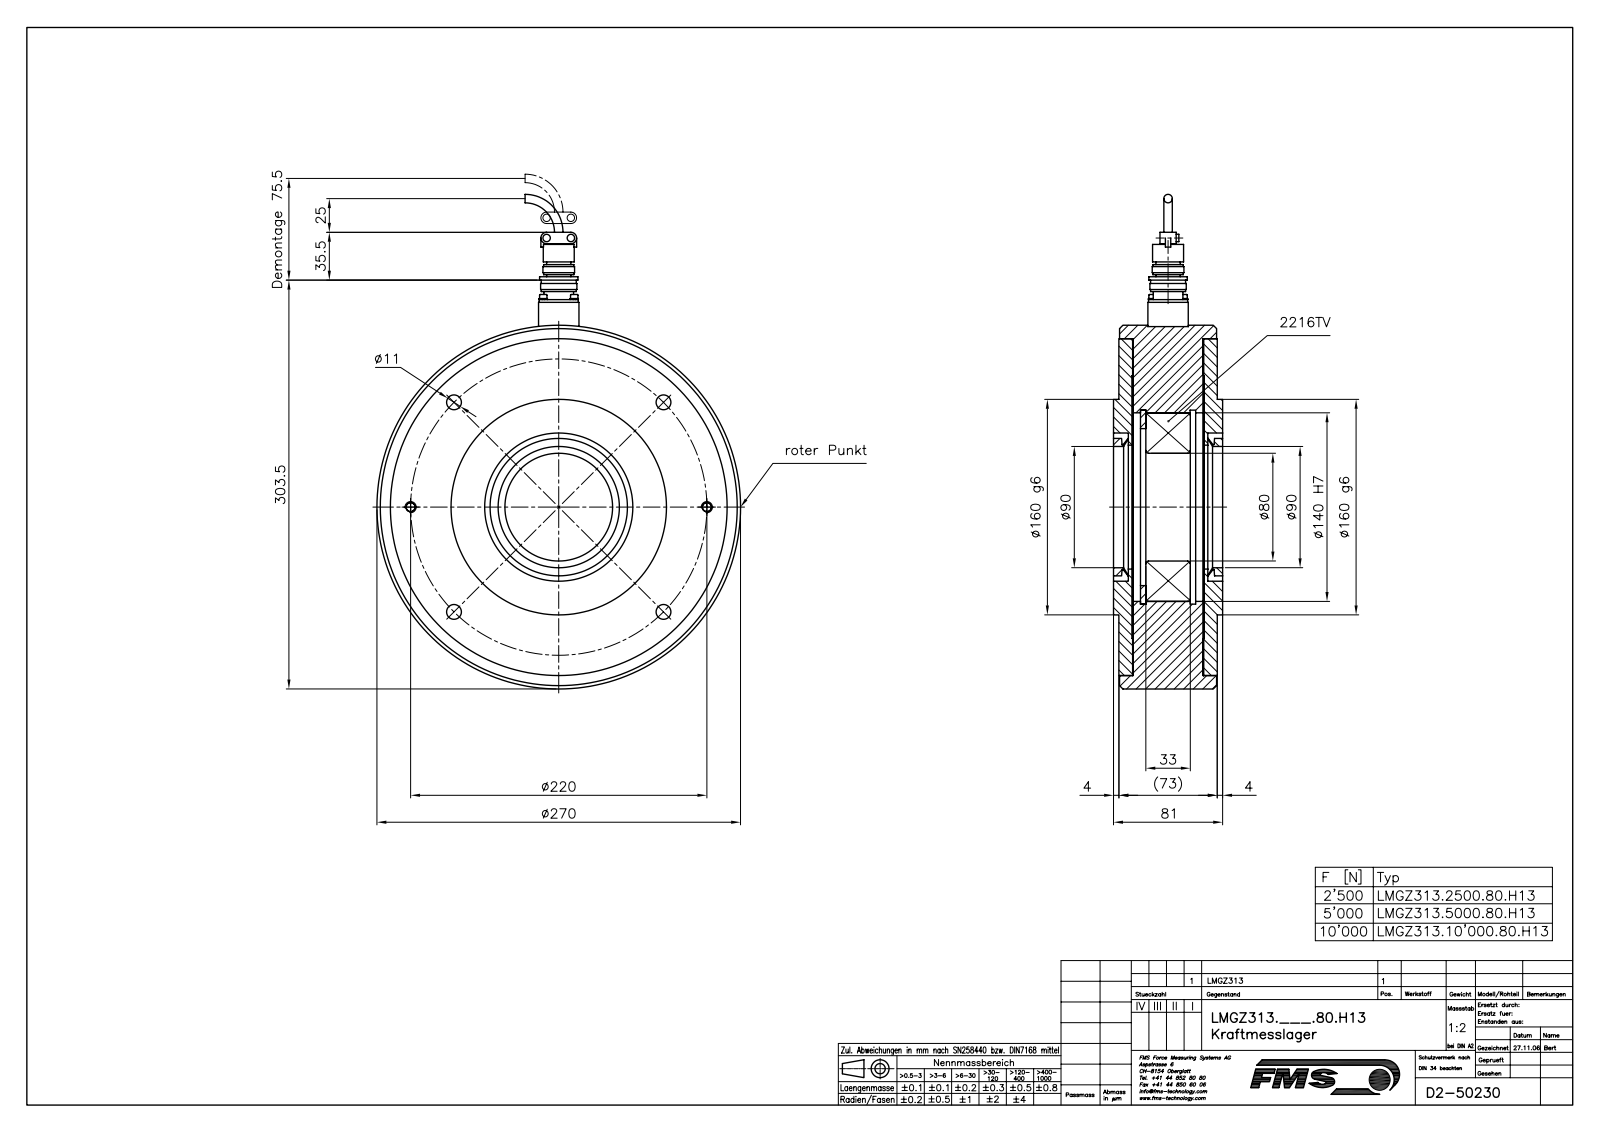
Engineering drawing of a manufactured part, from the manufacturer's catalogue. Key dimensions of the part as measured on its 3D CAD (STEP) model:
Part name (STEP PRODUCT): L50230; L4926704; TEIL1; L49342 (+8 more)
STEP written by: Mechanical Desktop 2007 (CONFIG_CONTROL_DESIGN)
Units: millimetres
Bodies: 21 solids, 398 faces (104 planar, 232 cylindrical, 62 other)
Overall size (bounding box): 367.15 × 320.5 × 270
Volume: 3 620 000 mm³ · Surface area: 569 668 mm²
Round holes (diameter × count): ⌀2.6 ×4, ⌀3.2 ×4, ⌀3.4 ×4, ⌀11 ×4, ⌀12 ×4, ⌀6.91 ×2, ⌀9 ×2, ⌀10 ×2, ⌀15 ×2, ⌀23 ×1, ⌀80 ×1, ⌀90 ×1
Round bosses / shafts (diameter × count): ⌀5.5 ×6, ⌀6.2 ×4, ⌀3 ×4, ⌀2.5 ×4, ⌀13 ×2, ⌀8 ×2, ⌀270 ×1, ⌀250 ×1
Partial cylindrical surfaces — rounded edges, fillets, slot ends (radius × count): R4.25 ×2
Main face-to-face distances: 52.3, 62.8, 0.5, 9.7, 10.5, 10.2, 62.5, 52, 0.8, 63.3
Hole centre spacings: 110, 16.26, 23, 84.19, 155.56, 203.25, 220, 32.53
